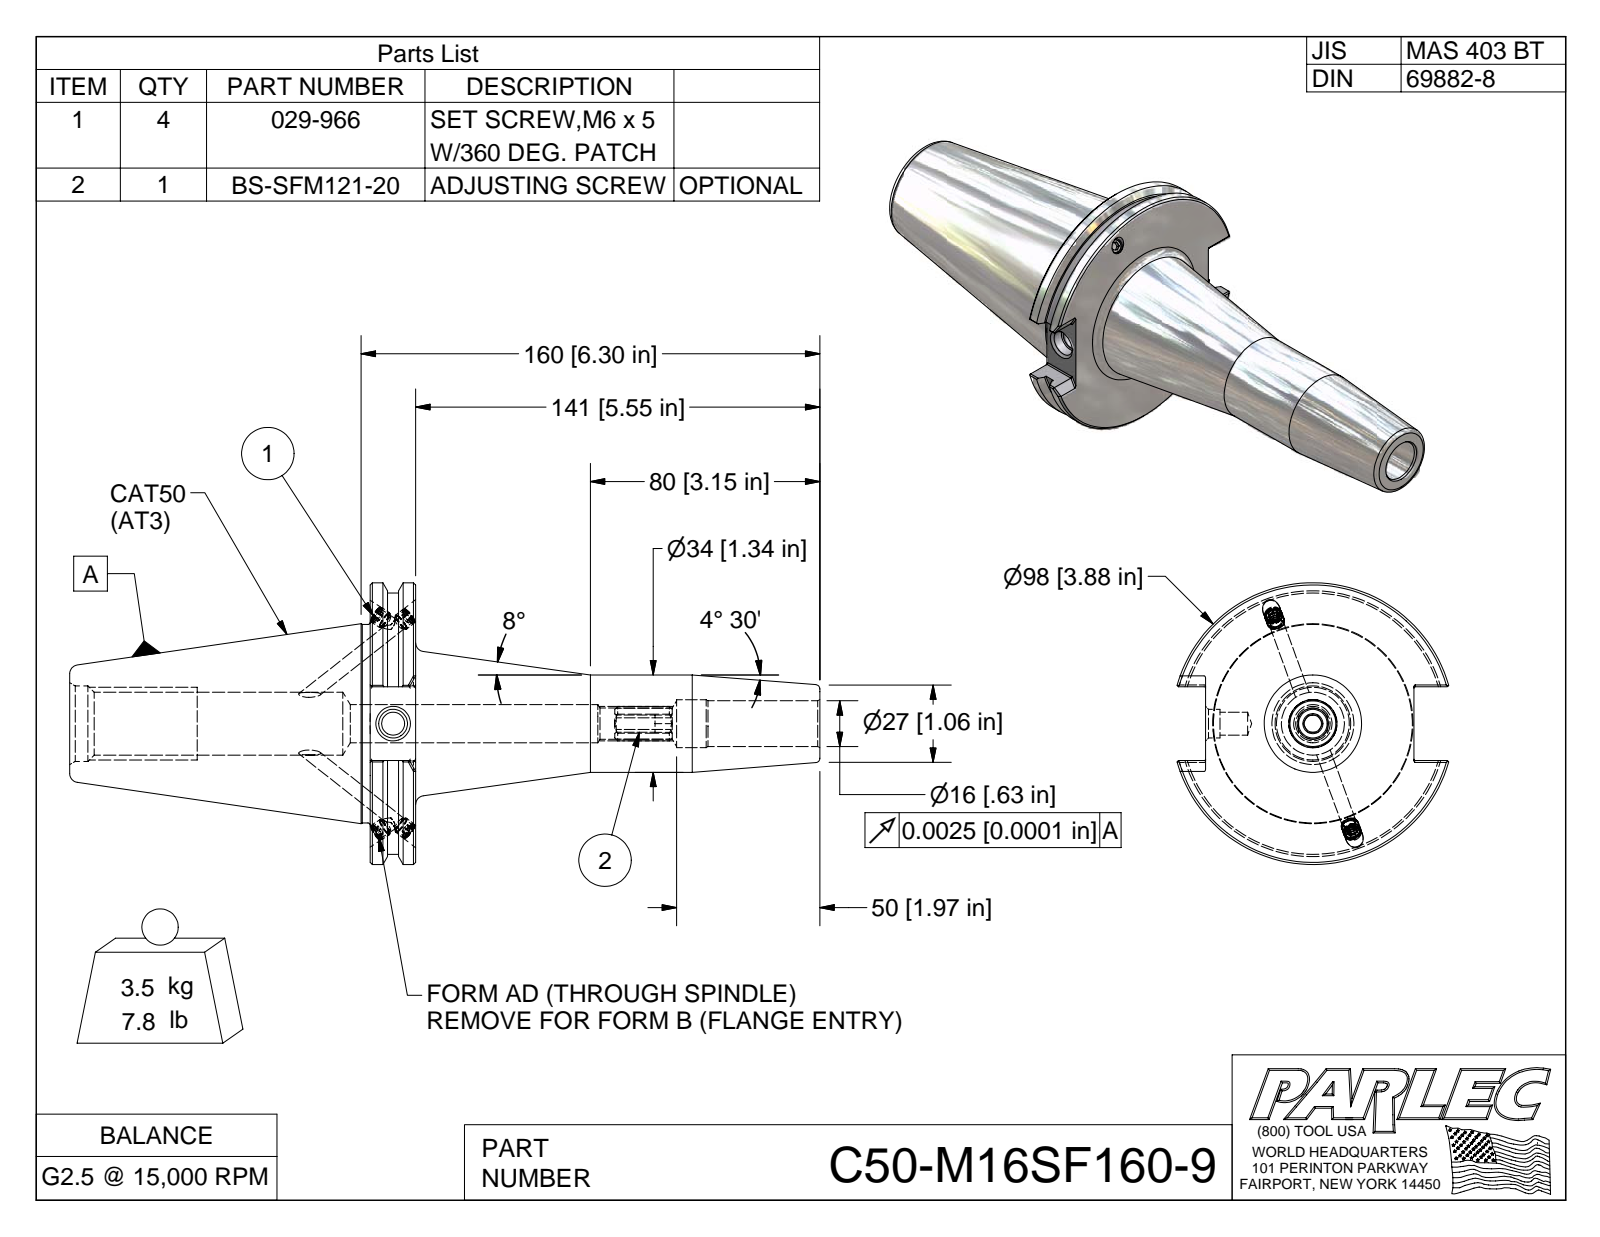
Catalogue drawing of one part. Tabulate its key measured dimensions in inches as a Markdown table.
| quantity | value |
| --- | --- |
| part name | C50-M16SF160-9; C50BC-M16SF160-9-1; BS-SFM121-20; 029-966 |
| STEP written by | Autodesk Inventor 2009 (AUTOMOTIVE_DESIGN) |
| units | inches |
| bodies | 6 solids, 187 faces (87 planar, 44 cylindrical, 56 other) |
| overall size | 10.299 × 3.875 × 3.729 |
| volume | 27.7 in³ |
| surface area | 105.3 in² |
| round holes (diameter × count) | 0.197 × 4, 0.24 × 4, 0.629 × 1, 0.659 × 1 |
| round bosses / shafts (diameter × count) | 0.244 × 4, 0.236 × 4, 3.875 × 1, 3.594 × 1, 2.73 × 1, 1.339 × 1 |
| partial cylindrical surfaces (radius × count) | 0.02 × 12, 0.236 × 1 |
| main face-to-face distances | 0.625, 4.125, 4.75, 2.86, 1.015, 10.299, 6.174, 5.549, 0.236, 0.389 |
